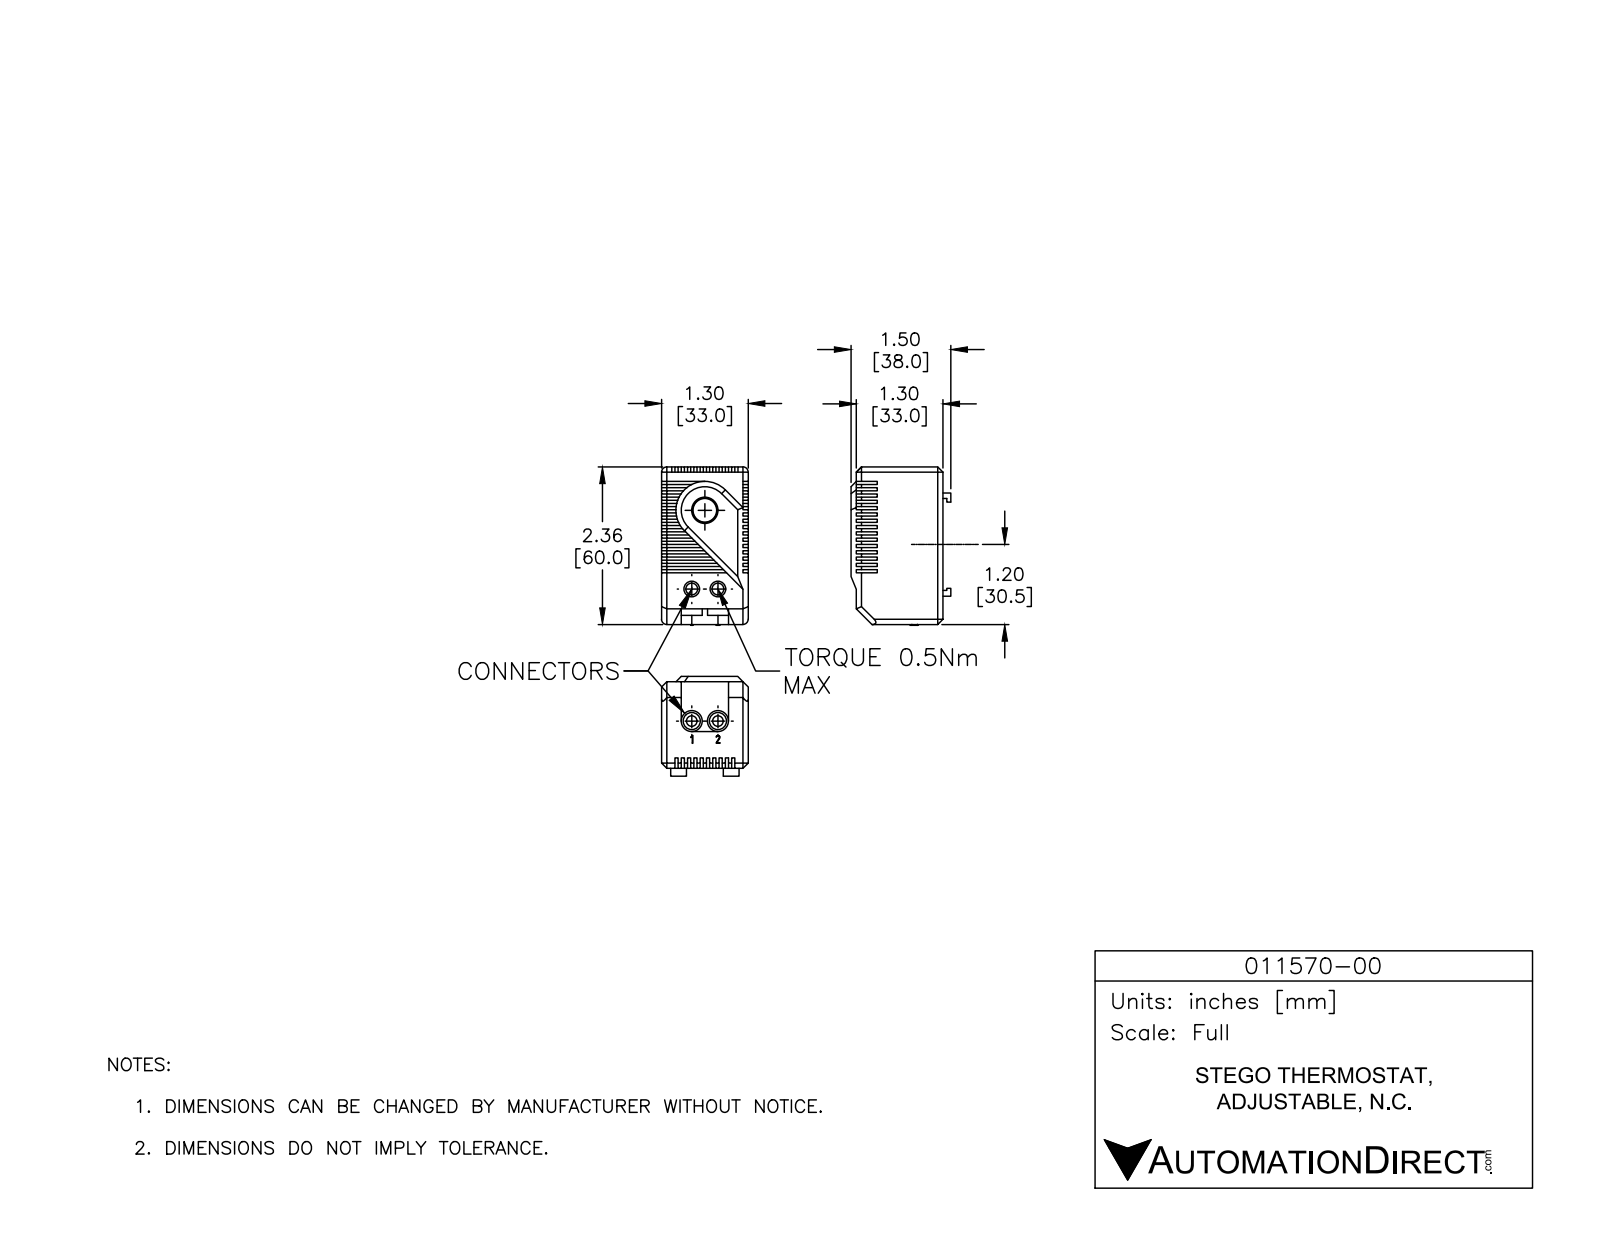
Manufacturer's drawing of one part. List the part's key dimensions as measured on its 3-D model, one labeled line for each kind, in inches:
Part name (STEP PRODUCT): 011570-00
STEP written by: SolidWorks 2017 (AUTOMOTIVE_DESIGN)
Units: inches
Bodies: 2 solids, 662 faces (538 planar, 40 cylindrical, 84 other)
Overall size (bounding box): 2.374 × 1.496 × 1.317
Volume: 3.757 in³ · Surface area: 21.36 in²
Round holes (diameter × count): ⌀0.157 ×2, ⌀0.177 ×2, ⌀0.236 ×2, ⌀0.256 ×2, ⌀0.394 ×1
Round bosses / shafts (diameter × count): ⌀0.315 ×2, ⌀0.37 ×1
Partial cylindrical surfaces — rounded edges, fillets, slot ends (radius × count): R0.079 ×4, R0.054 ×1, R0.06 ×1, R0.433 ×1
Main face-to-face distances: 1.299, 0.094, 0.047, 0.189, 0.236, 0.142, 0.079, 0.283, 0.378, 0.331
Hole centre spacings: 0.394, 1.197
